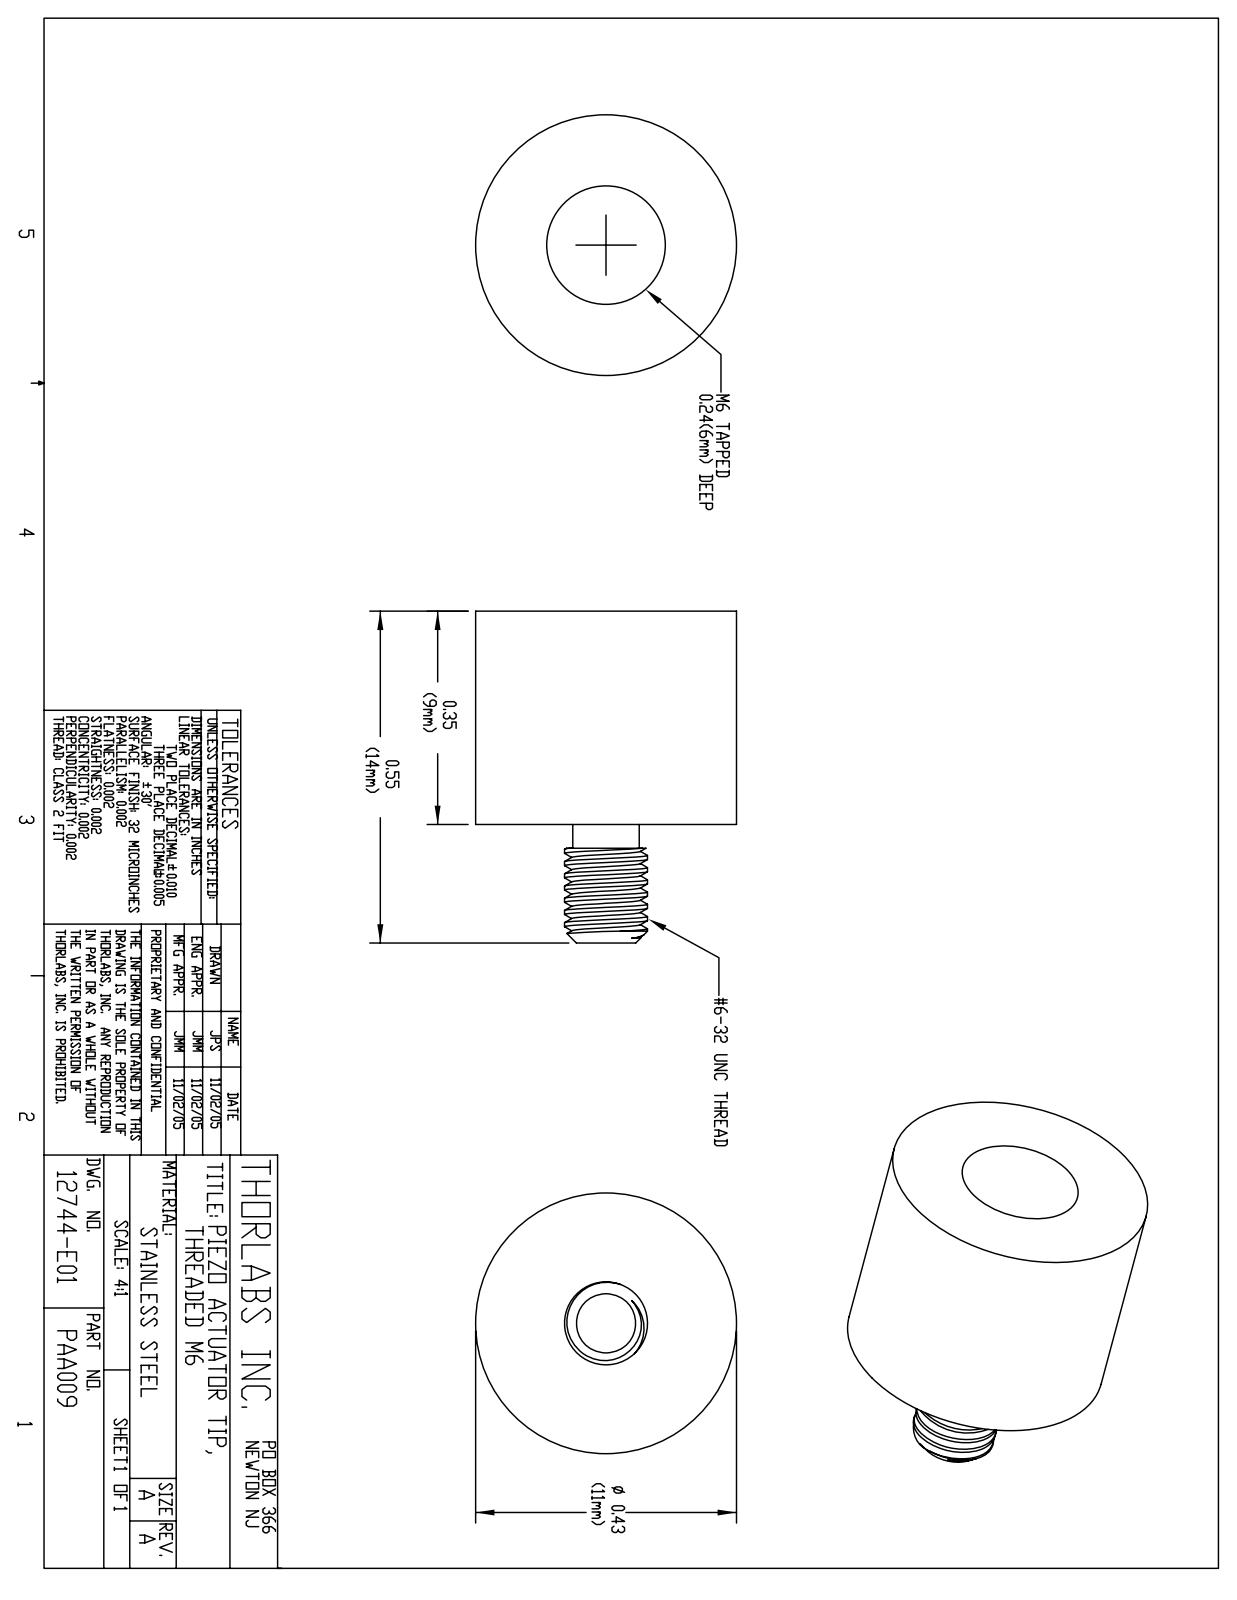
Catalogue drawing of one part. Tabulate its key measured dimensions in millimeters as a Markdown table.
| quantity | value |
| --- | --- |
| part name | 12744-E0W |
| STEP written by | SolidWorks 2007 (AUTOMOTIVE_DESIGN) |
| units | millimeters |
| bodies | 0 solids, 28 faces (3 planar, 21 cylindrical, 4 other) |
| overall size | 14 × 11 × 11 |
| round holes (diameter × count) | 5 × 1 |
| round bosses / shafts (diameter × count) | 11 × 1, 3.5 × 1, 2.8 × 1 |
| main face-to-face distances | 9, 14, 5 |
